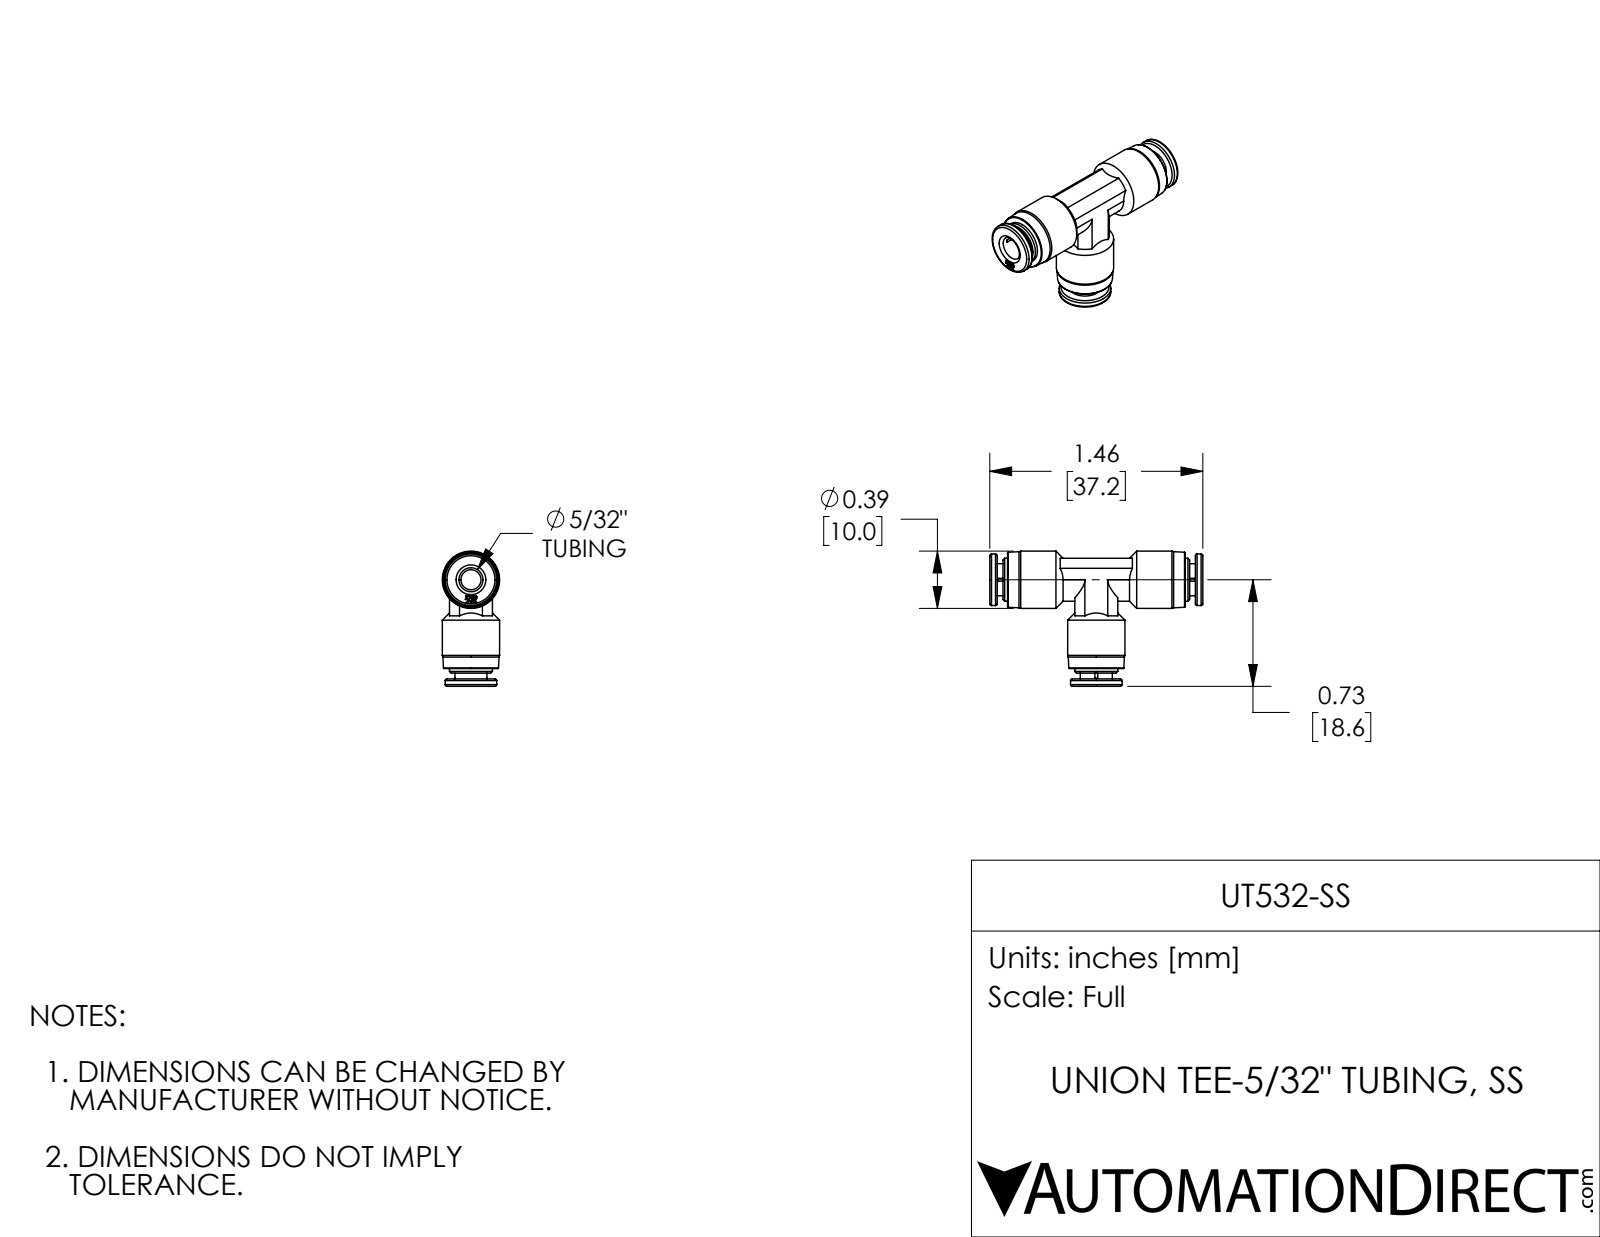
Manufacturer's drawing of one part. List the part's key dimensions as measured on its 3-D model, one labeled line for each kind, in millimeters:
Part name (STEP PRODUCT): UT532-SS
STEP written by: SolidWorks 2017 (AUTOMOTIVE_DESIGN)
Units: millimetres
Bodies: 1 solid, 311 faces (110 planar, 43 cylindrical, 158 other)
Overall size (bounding box): 37.24 × 23.6 × 10
Volume: 2 572 mm³ · Surface area: 2 626 mm²
Round holes (diameter × count): ⌀3.5 ×2, ⌀4.2 ×2
Round bosses / shafts (diameter × count): ⌀10 ×2, ⌀9 ×2, ⌀7.5 ×2, ⌀5.6 ×2
Partial cylindrical surfaces — rounded edges, fillets, slot ends (radius × count): R4.25 ×2
Main face-to-face distances: 1.3, 1.8, 3.1, 35.9, 7.5, 34.1, 32.8, 22.35, 21.05, 19.25
